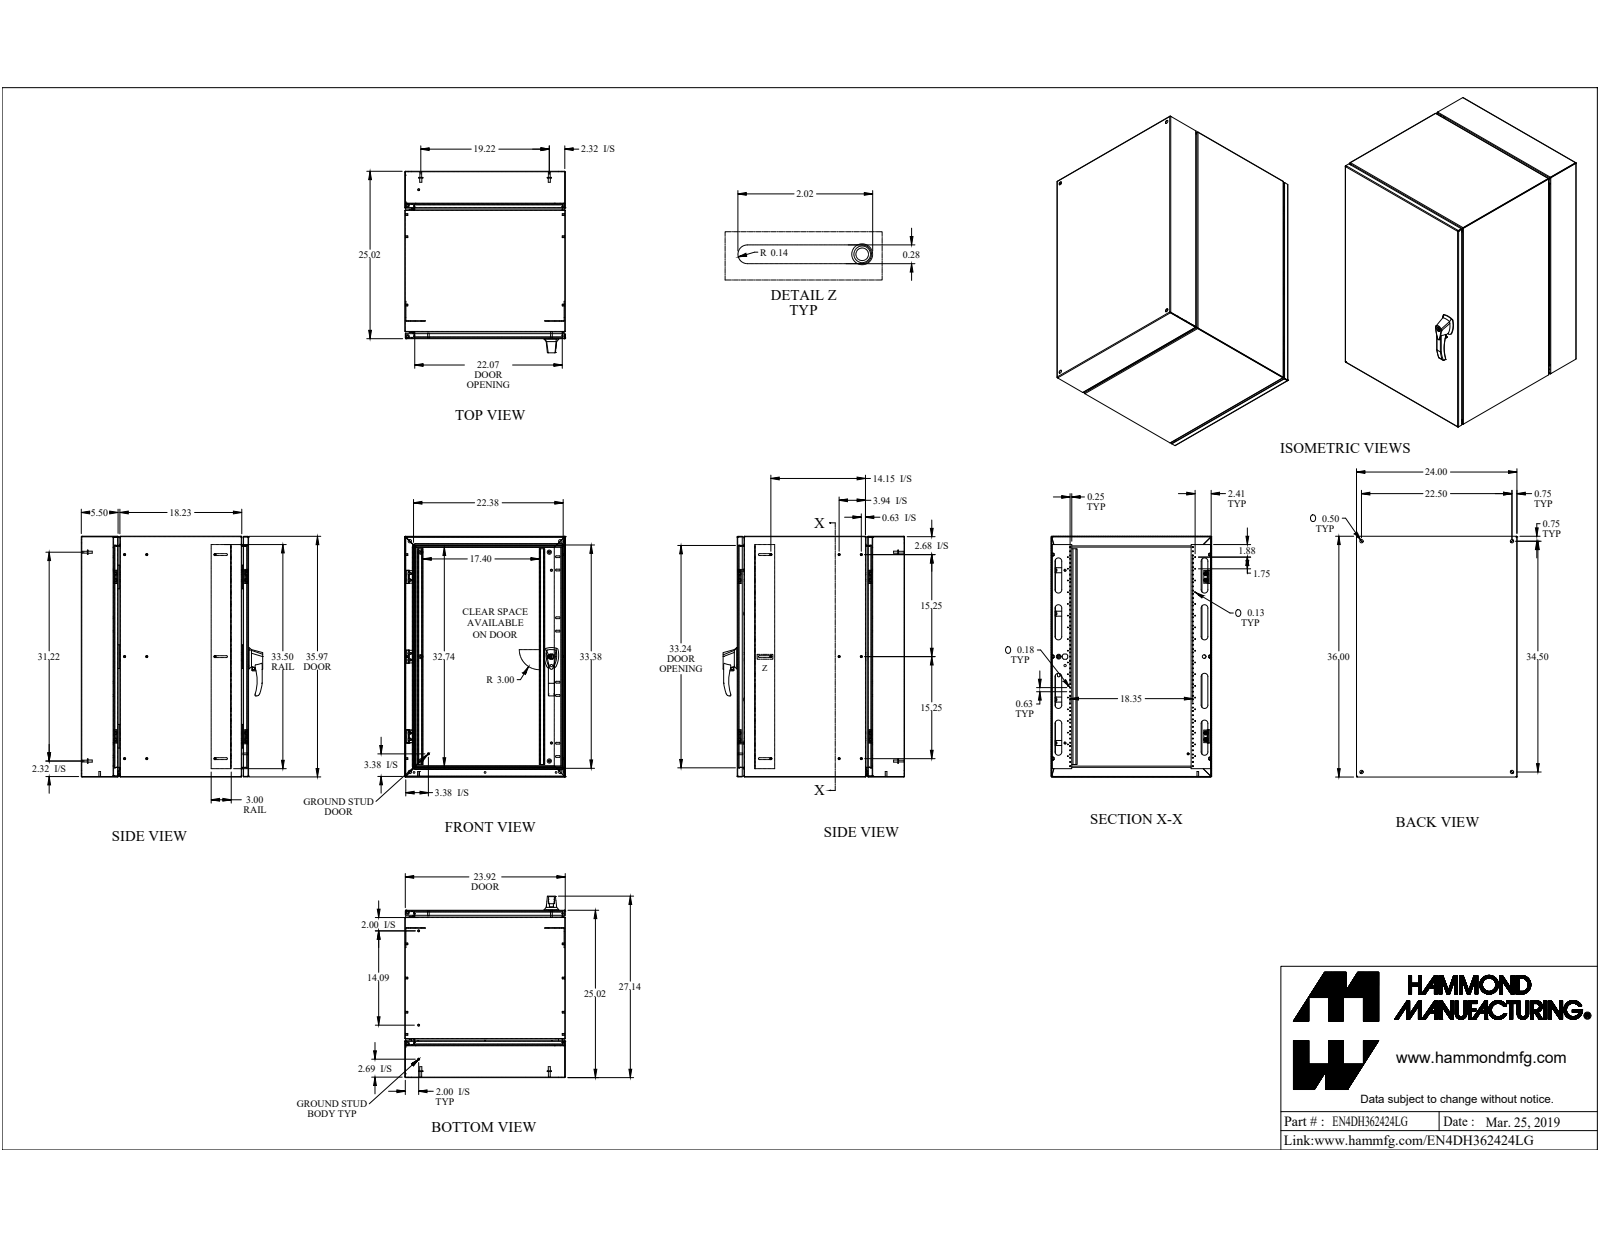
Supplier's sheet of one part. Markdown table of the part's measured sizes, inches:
| quantity | value |
| --- | --- |
| part name | EN4DH362424LG |
| STEP written by | SolidWorks 2019 (CONFIG_CONTROL_DESIGN) |
| units | inches |
| bodies | 240 solids, 4830 faces (2600 planar, 1295 cylindrical, 935 other) |
| overall size | 36 × 27.135 × 24.001 |
| volume | 499.7 in³ |
| surface area | 13 170 in² |
| round holes (diameter × count) | 0.177 × 114, 0.125 × 36, 0.25 × 23, 0.196 × 19, 0.188 × 14, 0.194 × 14, 0.237 × 14, 0.257 × 9, 0.275 × 9, 0.276 × 8, 0.265 × 7, 0.281 × 6 |
| round bosses / shafts (diameter × count) | 0.25 × 30, 0.313 × 18, 0.236 × 16, 0.472 × 14, 0.433 × 14, 0.187 × 14, 0.625 × 13, 0.281 × 8 |
| partial cylindrical surfaces (radius × count) | 0.036 × 37, 0.108 × 37, 0.25 × 26, 0.125 × 25, 0.06 × 24, 0.122 × 20, 0.129 × 19, 0.141 × 18 |
| main face-to-face distances | 0.072, 24.948, 23.928, 35.928, 23.856, 24.876, 25.02, 24, 35.856, 36 |
| hole center spacings | 20.382, 0.985, 11.906, 11.907, 15.25, 11.906, 13.523, 21.985 |
